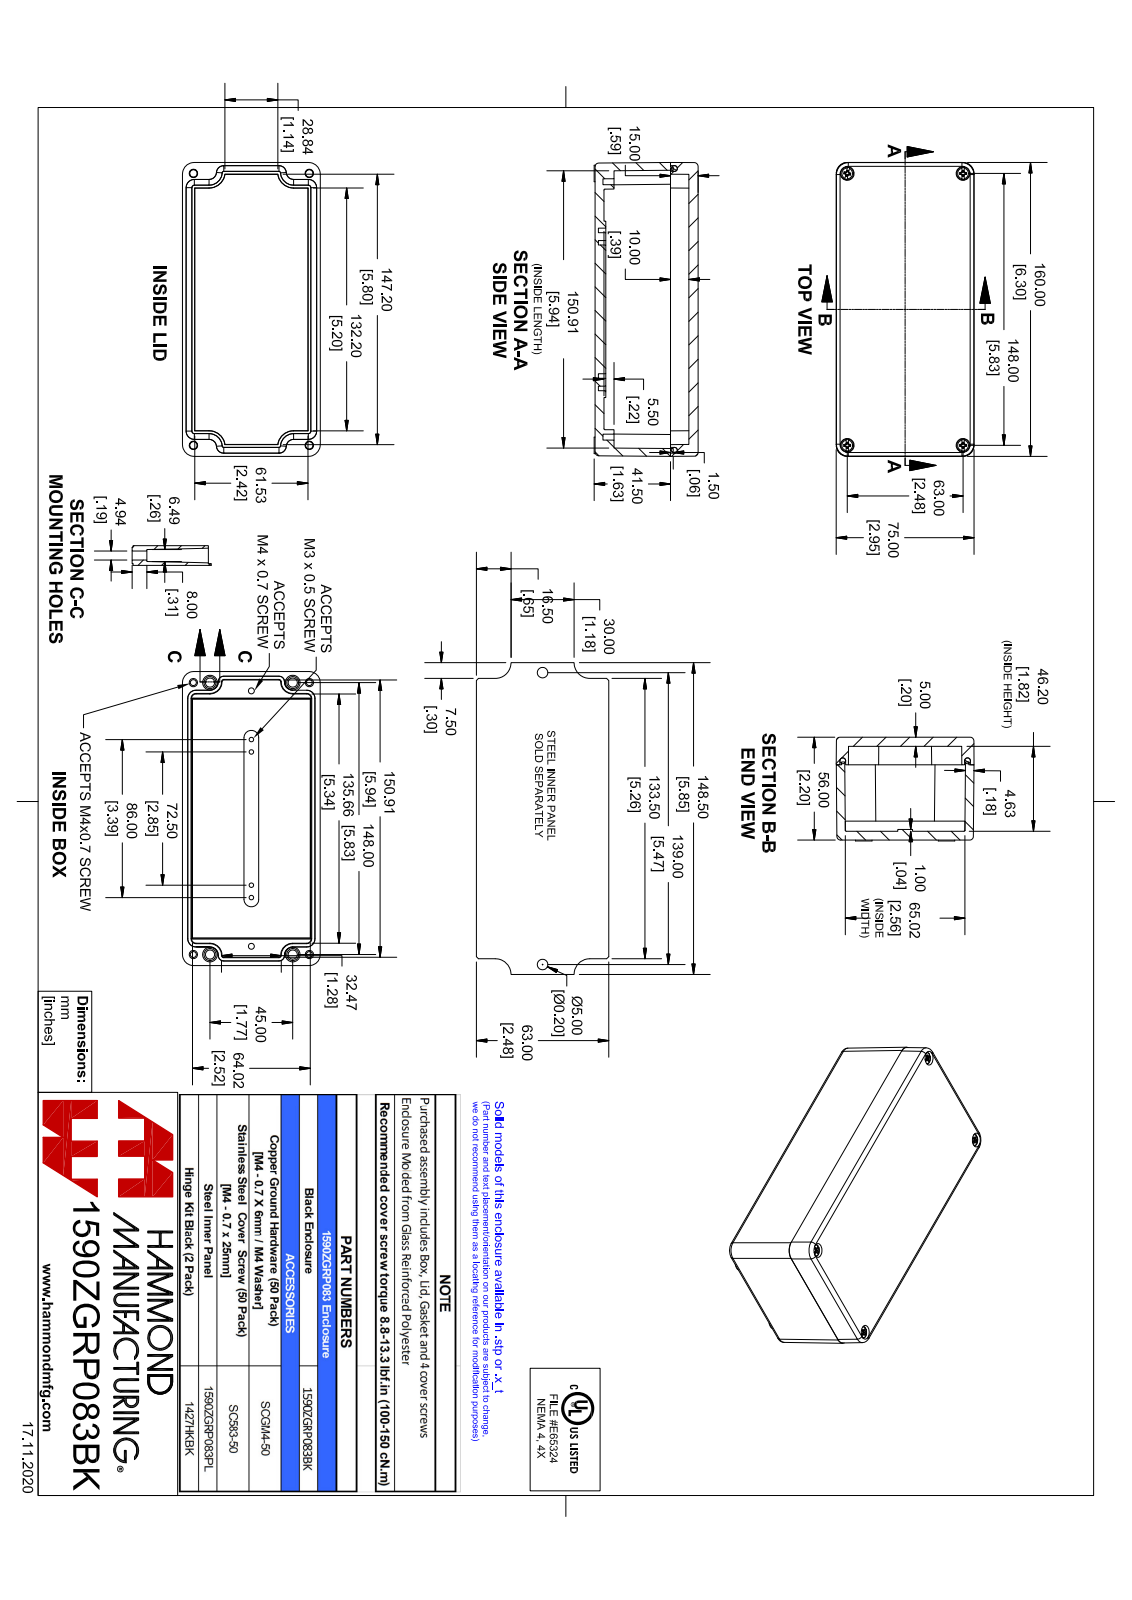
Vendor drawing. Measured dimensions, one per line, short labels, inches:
name: 1590ZGRP083BK
written by: SolidWorks 2021 (AUTOMOTIVE_DESIGN)
unit: in
bodies: 7 solids, 421 faces (213 planar, 80 cylindrical, 128 other)
size: 6.299 × 2.953 × 2.224
volume: 14.43 in³; area: 164.9 in²
holes: 6× ⌀0.128, 4× ⌀0.097, 4× ⌀0.161, 4× ⌀0.177, 4× ⌀0.197, 4× ⌀0.295
bosses: 7× ⌀0.126, 4× ⌀0.354, 4× ⌀0.272, 4× ⌀0.152, 4× ⌀0.137
rounds: 8× R0.079, 7× R0.061, 4× R0.02, 4× R0.236, 4× R0.256, 2× R0.157
face distances: 2.205, 0.182, 0.197, 2.008, 2.016, 0.189, 1.819, 2.951, 2.769, 0.394
hole spacings: 5.827, 0.354, 0.356, 0.904, 1.253, 1.255, 1.508, 1.73
